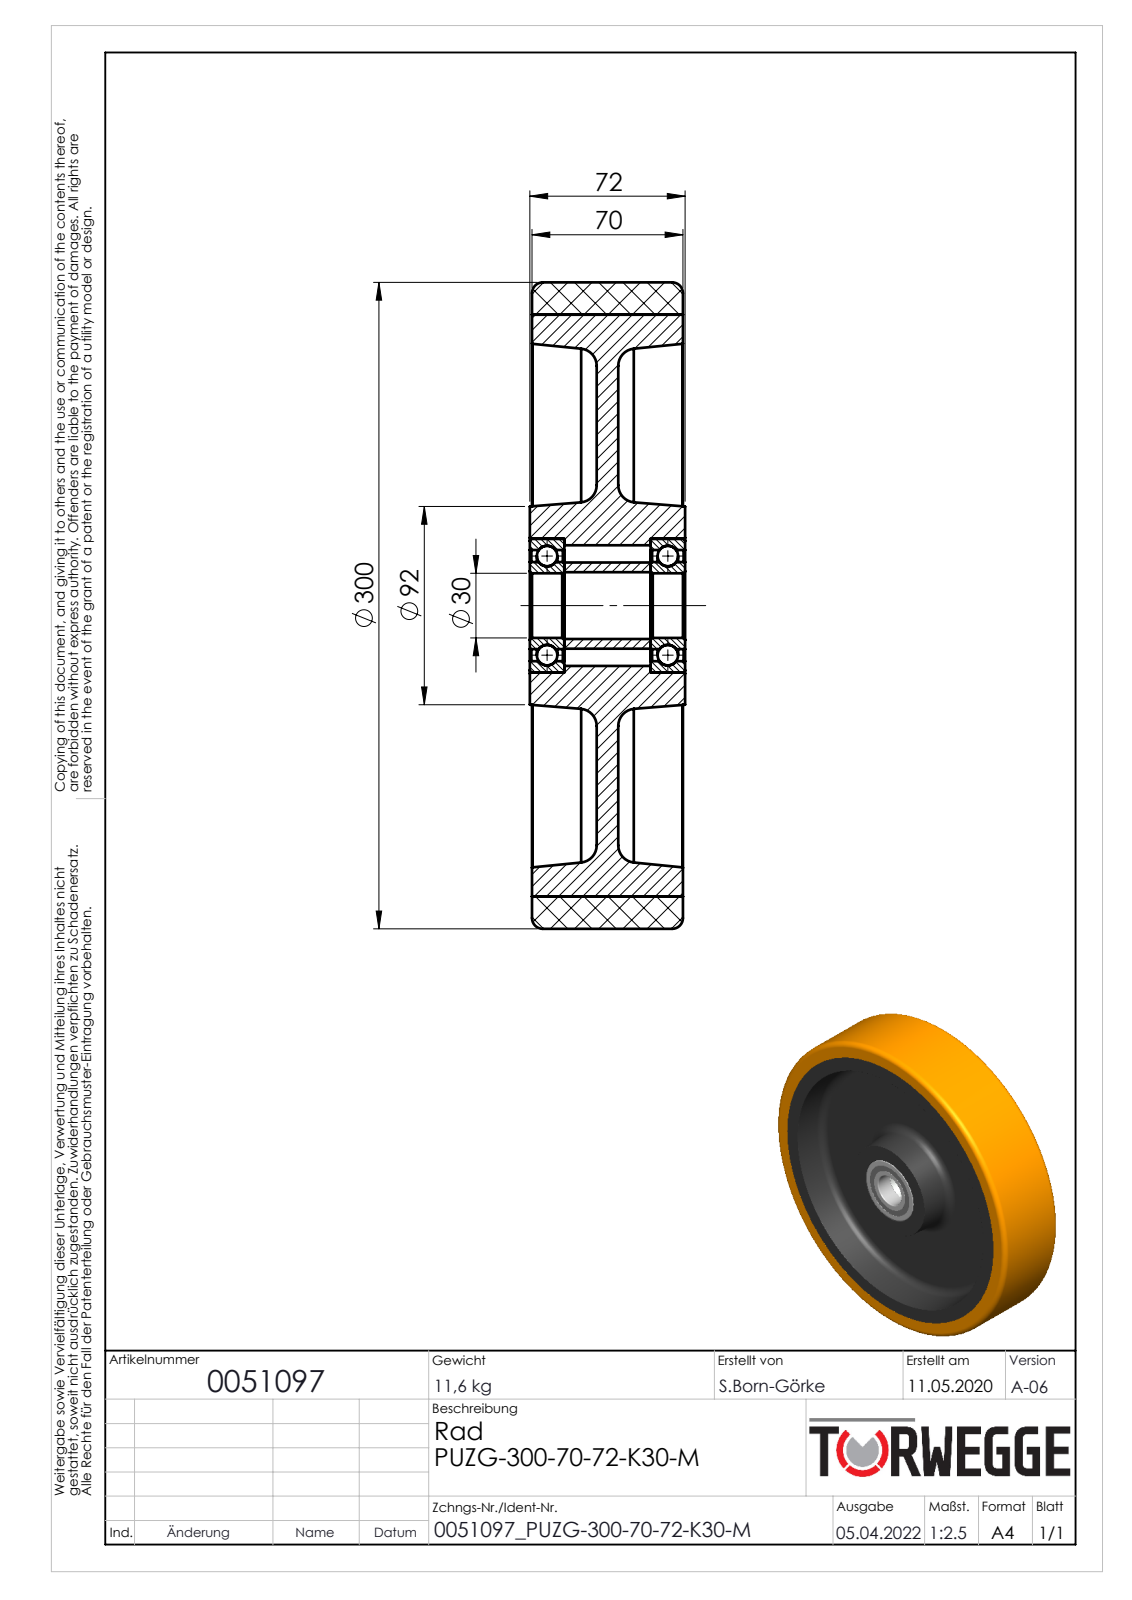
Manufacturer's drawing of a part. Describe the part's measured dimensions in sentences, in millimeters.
The part is named "0051097". Its 3-D file was written by "SolidWorks 2020 (AUTOMOTIVE_DESIGN)". It is 13 solids with 160 faces: 28 planar, 56 cylindrical and 76 other. Overall it measures 300 by 300 by 72.1 millimeters. Its volume is 2 570 000 cubic millimeters and its surface area 432 649 square millimeters. Round holes: 1 of diameter 30, 1 of diameter 31, 1 of diameter 40.4, 1 of diameter 51.6, 1 of diameter 56, 1 of diameter 62, 1 of diameter 270. Round bosses or shafts: 1 of diameter 300, 1 of diameter 40. The main face-to-face distances are 40, 30, 10, 70, 41, 1, 31, 71, 56.1, 56.05.
